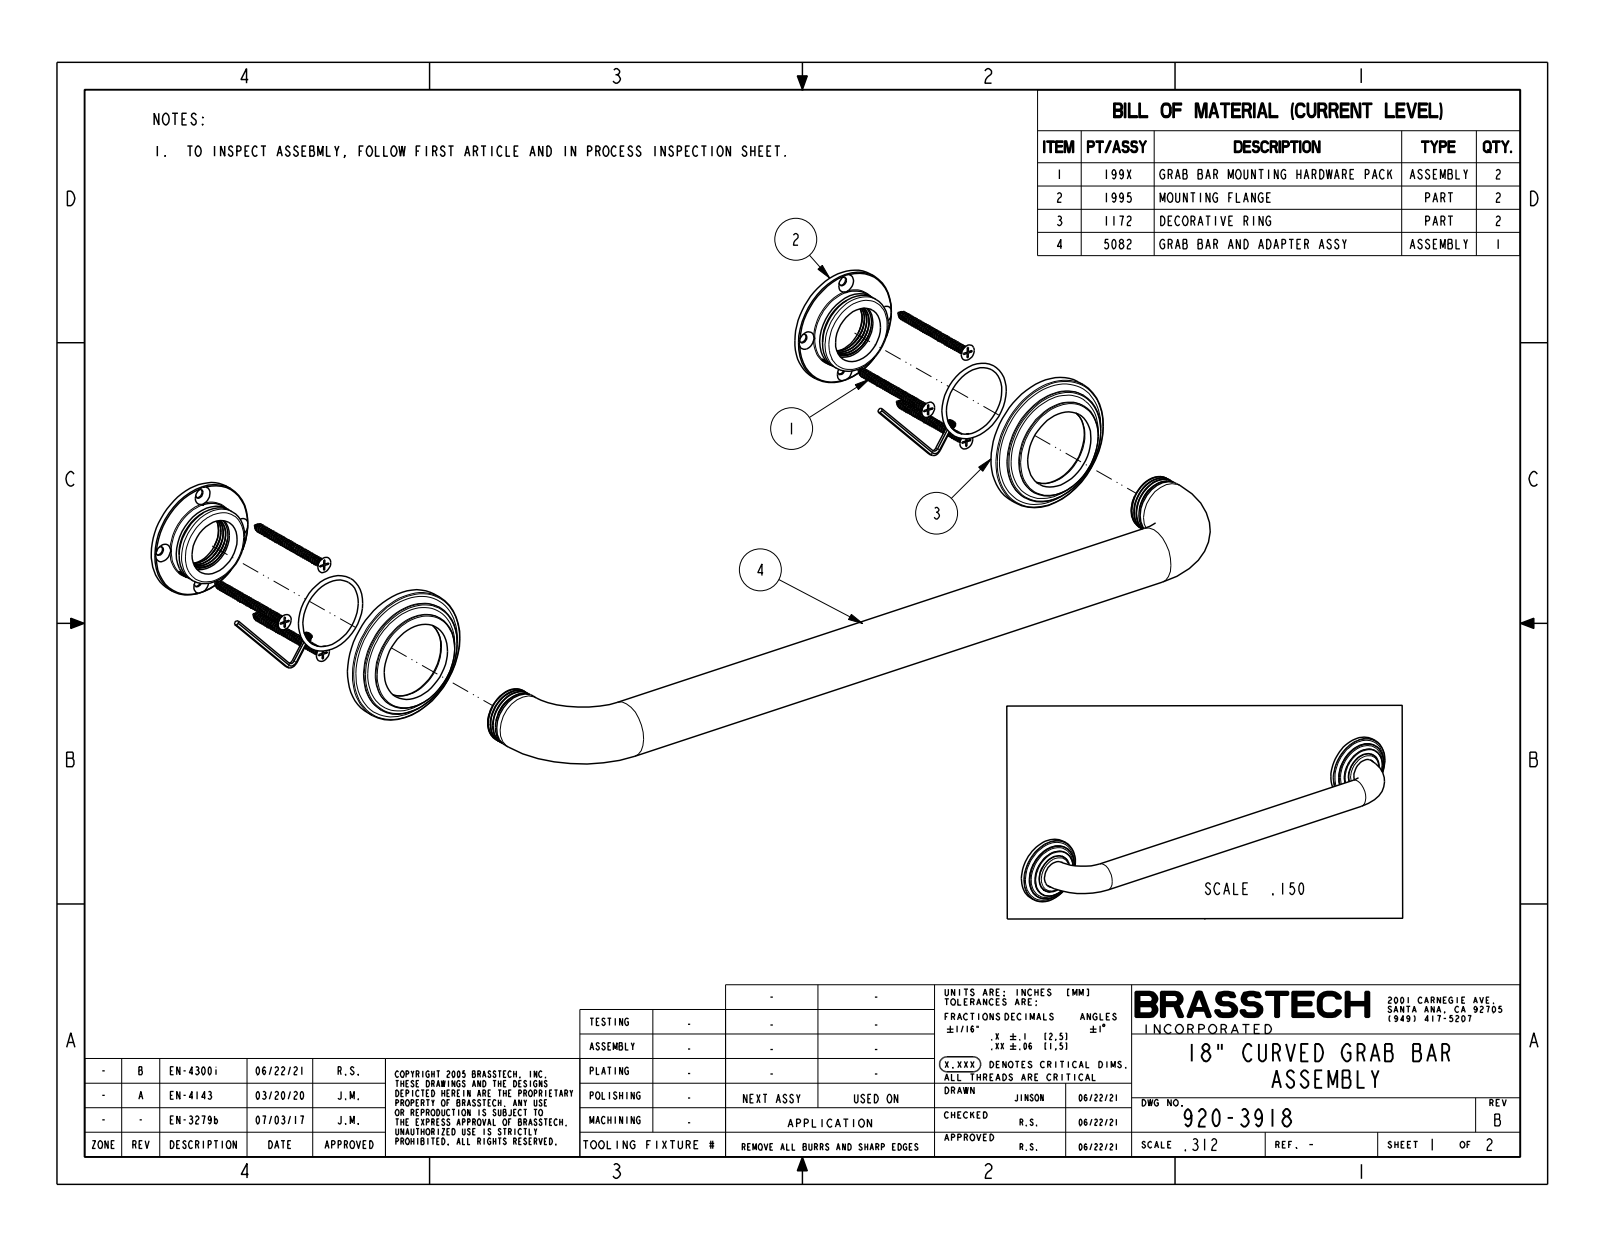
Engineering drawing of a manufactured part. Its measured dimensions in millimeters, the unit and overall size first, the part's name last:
Units: millimetres
Overall size (bounding box): 533.4 × 76.2 × 69.9
Round holes (diameter × count): ⌀5.1 ×8, ⌀29.3 ×3, ⌀4.1 ×2, ⌀22 ×2, ⌀29.5 ×2, ⌀32 ×2, ⌀45 ×2, ⌀72.2 ×2
Round bosses / shafts (diameter × count): ⌀31.8 ×3, ⌀76.2 ×2, ⌀66 ×2, ⌀55.9 ×2, ⌀49 ×2, ⌀44.5 ×2, ⌀40.5 ×2, ⌀31.4 ×2
Partial cylindrical surfaces — rounded edges, fillets, slot ends (radius × count): R5.4 ×8, R1 ×2
Main face-to-face distances: 3.8, 9.5, 13.3, 1.9, 11.4, 4.2, 15.2, 8.9, 2.5, 6.1
Hole centre spacings: 27.6, 39.1, 457.2, 55.2, 430.5, 458, 485.6, 429.6
Volume: 125 100 mm³ · Surface area: 215 400 mm²
Bodies: 7 solids, 676 faces (160 planar, 204 cylindrical, 312 other)
Part name (STEP PRODUCT): 1995; 20-287_ASM; 80528; 50869 (+3 more)
STEP written by: PRO/ENGINEER BY PARAMETRIC TECHNOLOGY CORPORATION, 2013150 (CONFIG_CONTROL_DESIGN)
